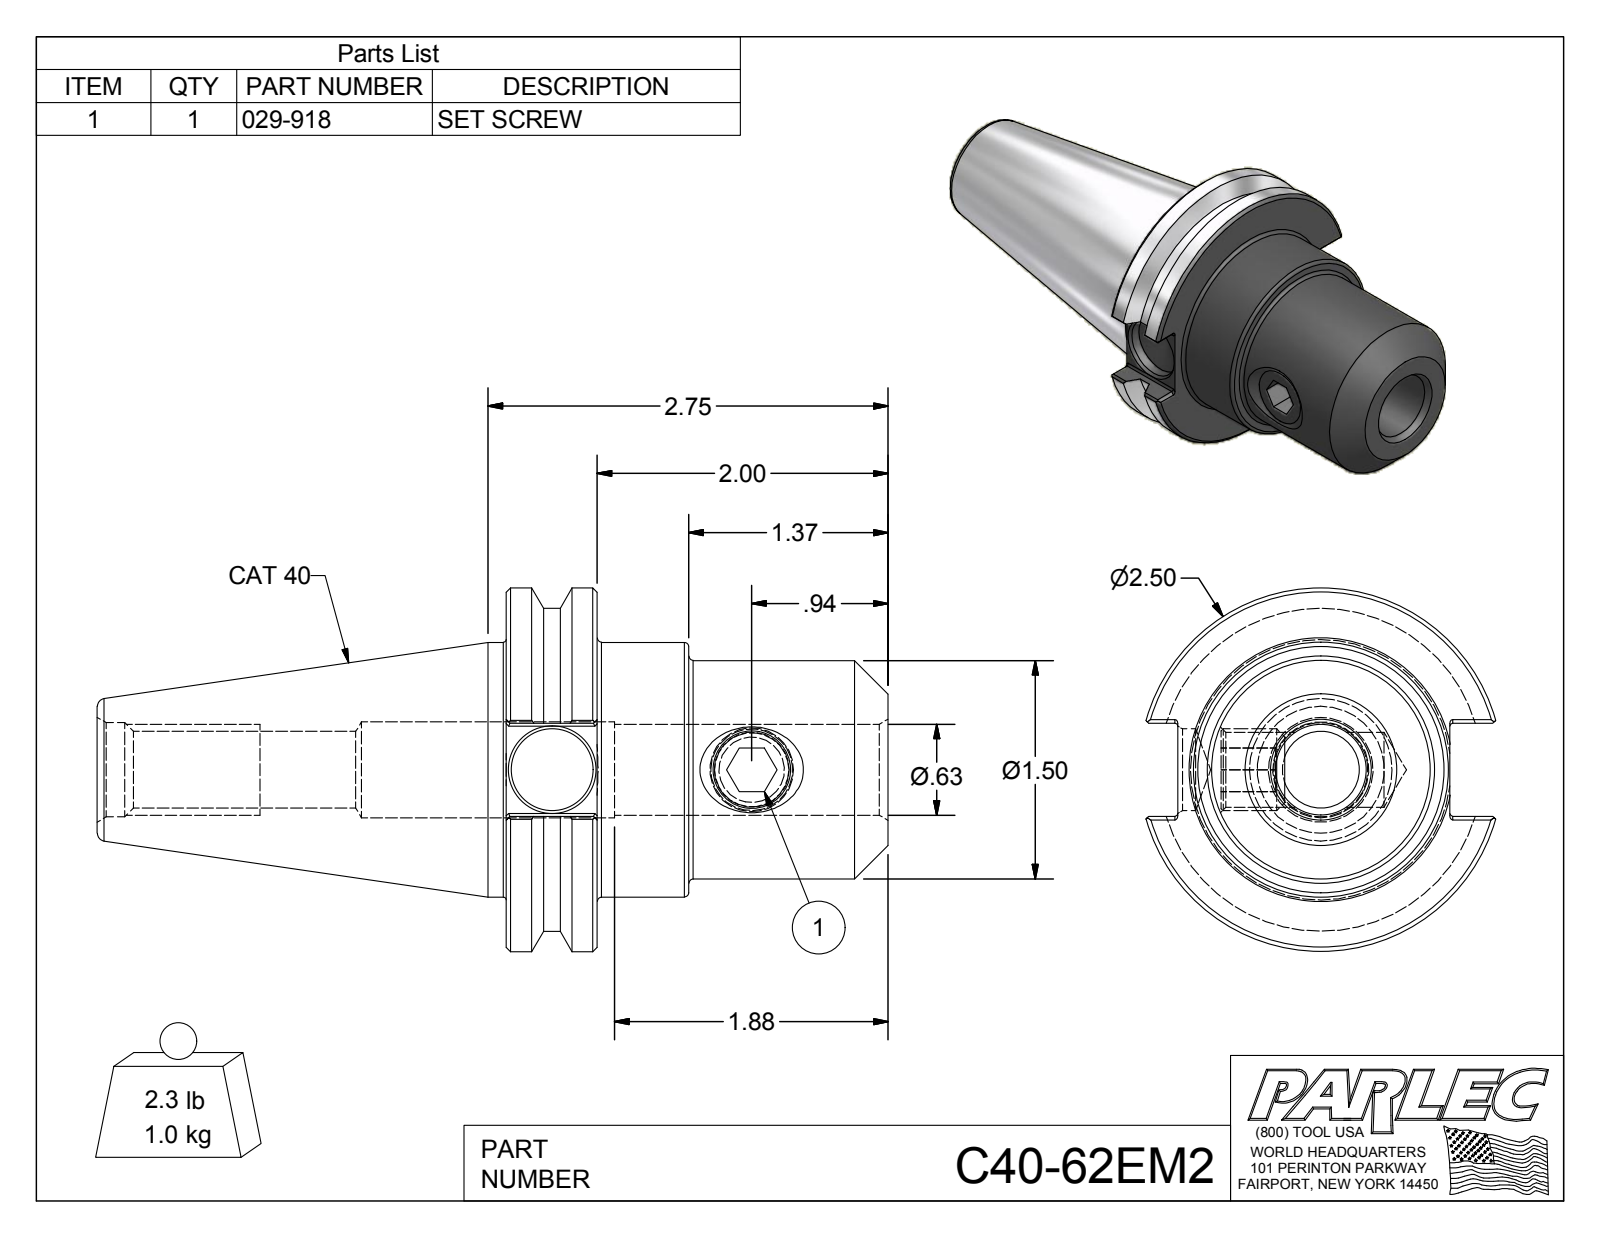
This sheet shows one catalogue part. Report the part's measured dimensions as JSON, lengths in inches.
{"part_name": "C40-62EM2; C40-62EM2-1; 029-918", "step_written_by": "Autodesk Inventor 2012 (AUTOMOTIVE_DESIGN)", "units": "inches", "bodies": {"solids": 2, "faces": 106, "planar": 42, "cylindrical": 30, "other": 34}, "overall_size": [5.437, 2.5, 2.406], "volume_in3": 9.06, "surface_area_in2": 47.04, "round_holes": [[0.315, 1], [0.399, 1], [0.516, 1], [0.527, 1], [0.625, 1], [0.648, 1], [0.66, 1]], "round_bosses_or_shafts": [[2.5, 1], [2.219, 1], [1.75, 1], [1.73, 1], [1.5, 1], [0.563, 1]], "partial_cylinders_radius": [[0.02, 12]], "face_to_face_distances": [0.625, 2.625, 2, 1.255, 0.63, 1.37, 0.64, 1.86, 0.3, 2.812], "hole_center_spacings": [1.372]}
